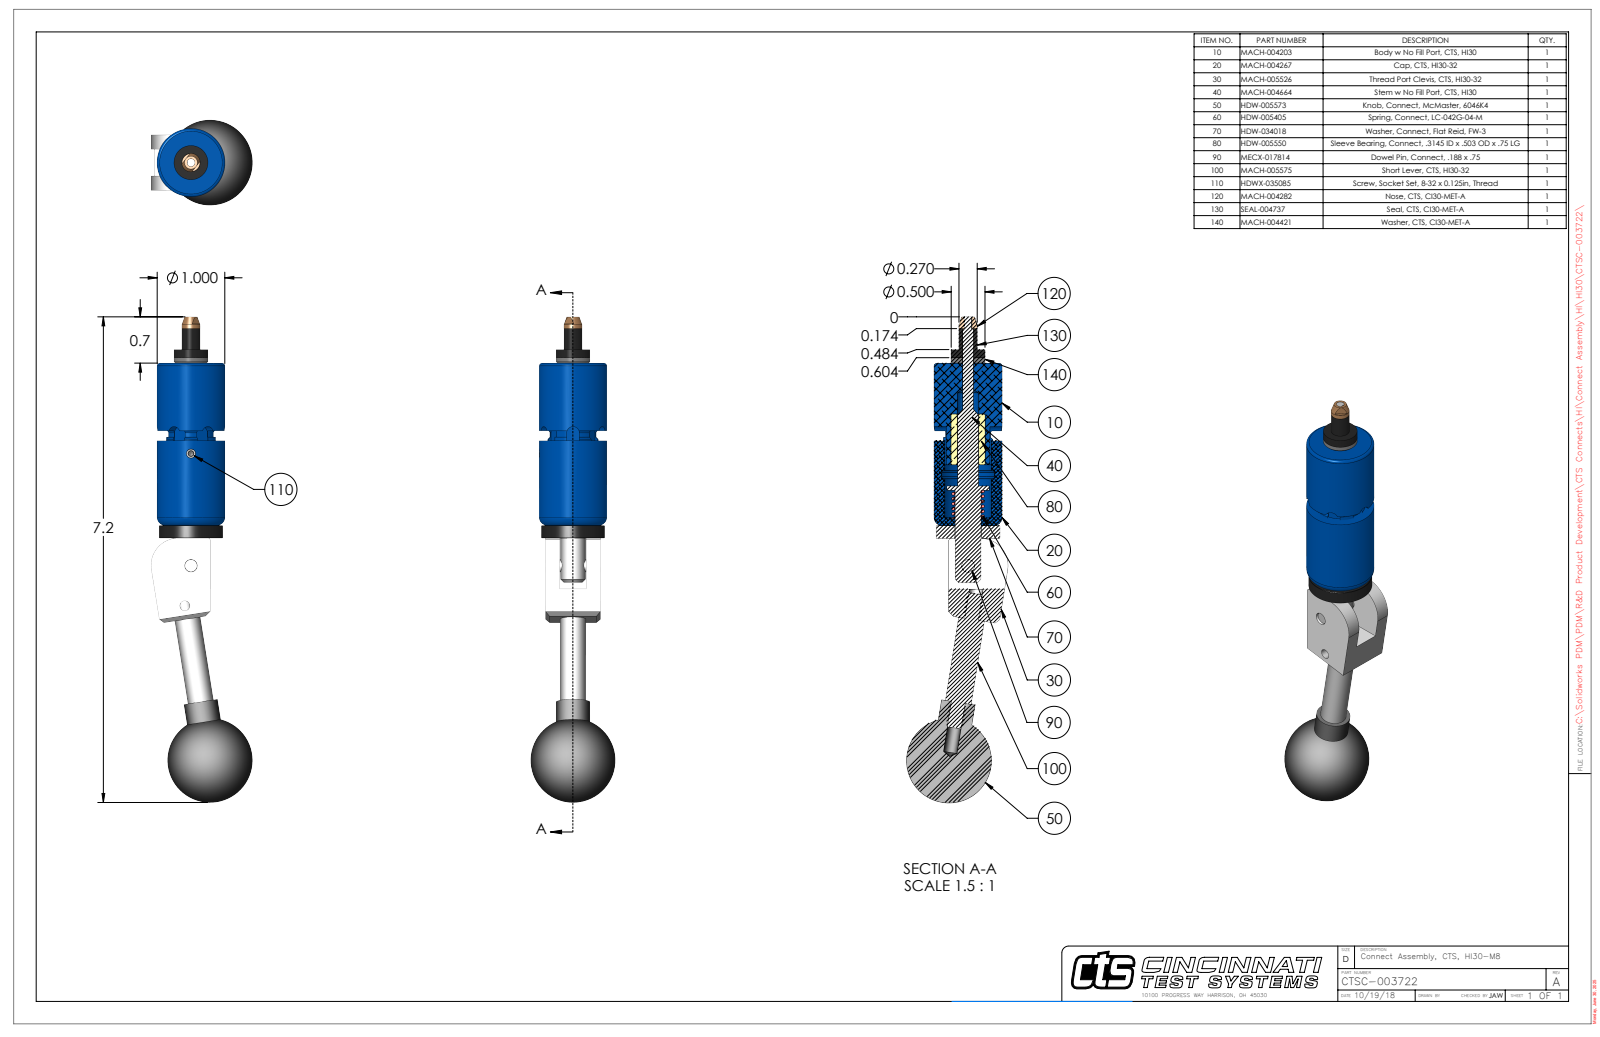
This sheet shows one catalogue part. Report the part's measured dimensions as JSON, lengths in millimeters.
{"part_name": "CTSC-003722", "step_written_by": "SolidWorks 2023 (AUTOMOTIVE_DESIGN)", "units": "millimeters", "bodies": {"solids": 9, "faces": 276, "planar": 105, "cylindrical": 111, "other": 60}, "overall_size": [182.4, 37.9, 31.8], "volume_mm3": 62370, "surface_area_mm2": 19410, "round_holes": [[5.1, 2], [2.9, 1], [3.5, 1], [3.8, 1], [3.9, 1], [4.1, 1], [4.2, 1], [4.8, 1], [9.8, 1], [10, 1], [17.5, 1]], "round_bosses_or_shafts": [[12.7, 2], [25.4, 1], [23.8, 1], [9.7, 1], [9.5, 1], [6.9, 1], [6.4, 1], [5.1, 1]], "partial_cylinders_radius": [[2.4, 6], [0.4, 1], [9.5, 1], [10.2, 1], [11.5, 1]], "face_to_face_distances": [5.3, 15.3, 20.6, 61, 65.7, 4.7, 9.9, 29.1, 31.8, 36.6], "hole_center_spacings": [15.2, 42.1, 57.2]}
